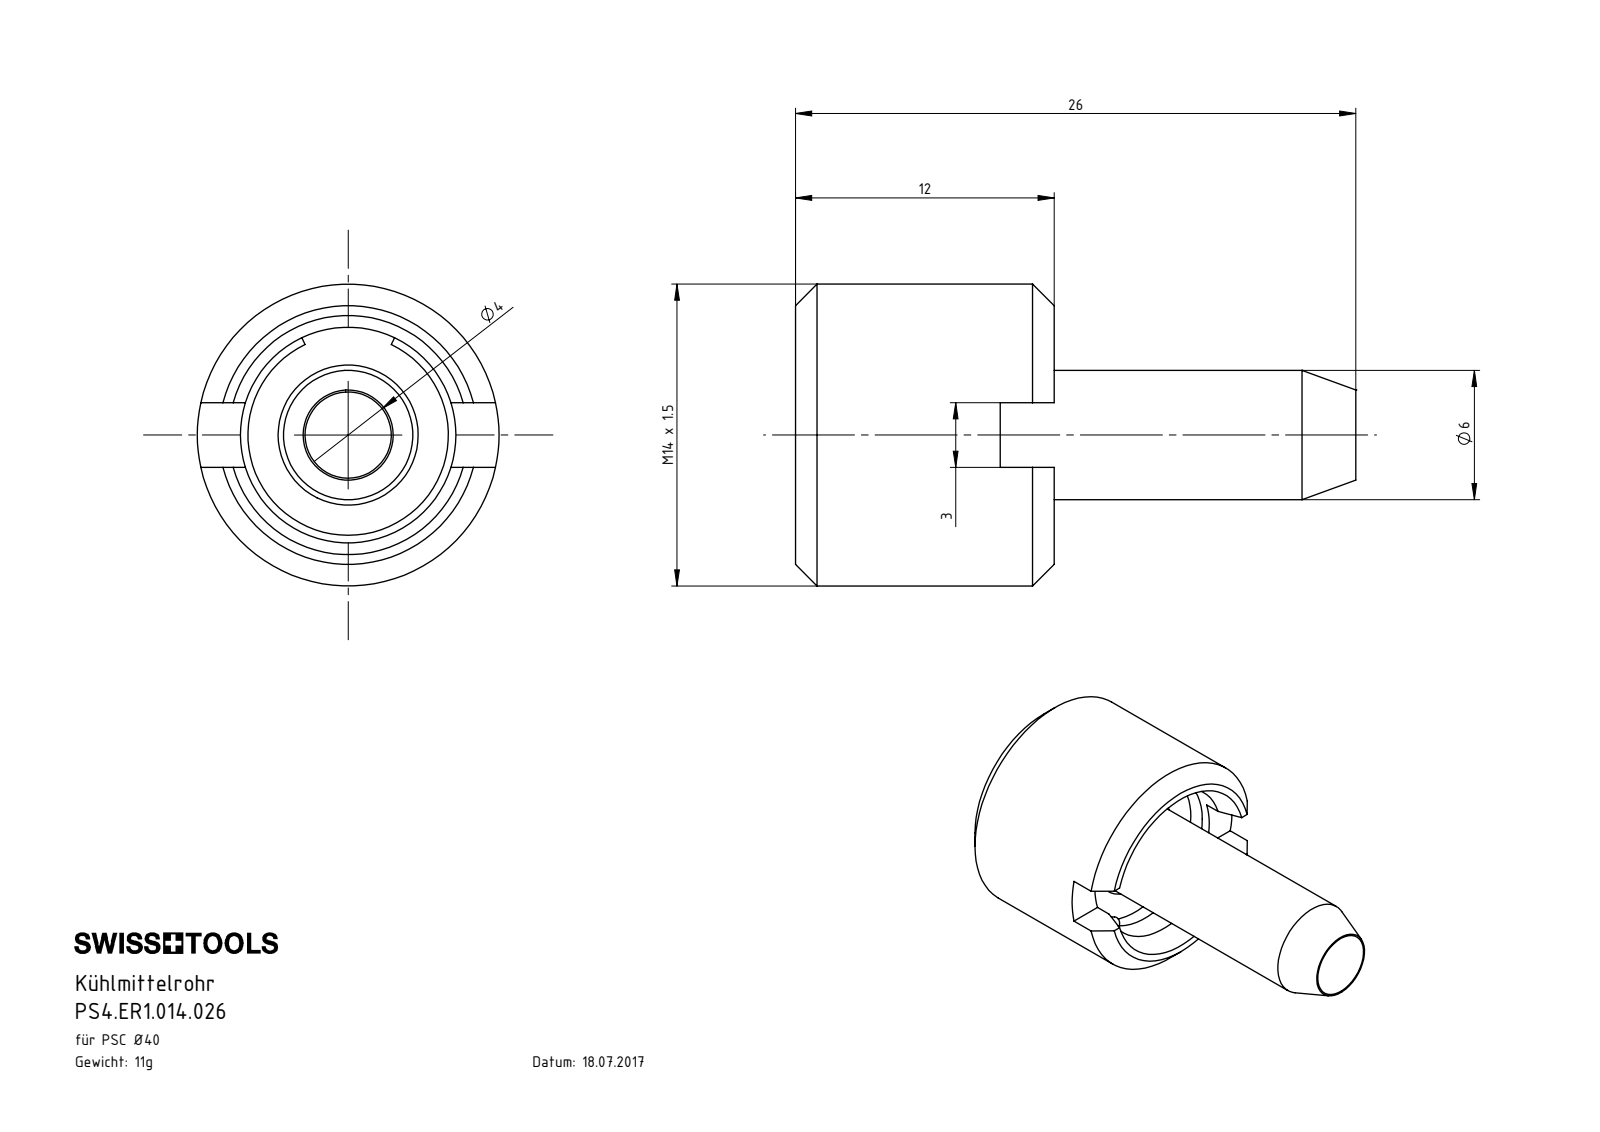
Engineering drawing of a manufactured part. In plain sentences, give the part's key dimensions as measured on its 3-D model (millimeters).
The part is named "PS4-ER1.009.024_A; PS4-ER1.014.012_A_Neu; DIN 3771 - 6x2; PS4-ER1.010.001_A (+2 more)". Its 3-D file was written by "SolidWorks 2017 (CONFIG_CONTROL_DESIGN)". It is 6 solids with 68 faces: 18 planar, 20 cylindrical and 30 other. Overall it measures 26 by 14 by 14 millimeters. Its volume is 1 562 cubic millimeters and its surface area 2 475 square millimeters. Round holes: 1 of diameter 4, 1 of diameter 4.2, 1 of diameter 6.5, 1 of diameter 10. Round bosses or shafts: 1 of diameter 14, 1 of diameter 9, 1 of diameter 6. The main face-to-face distances are 1.5, 8, 1.75, 3.75, 7, 5.5, 6.5, 1, 3.25, 4.75.
